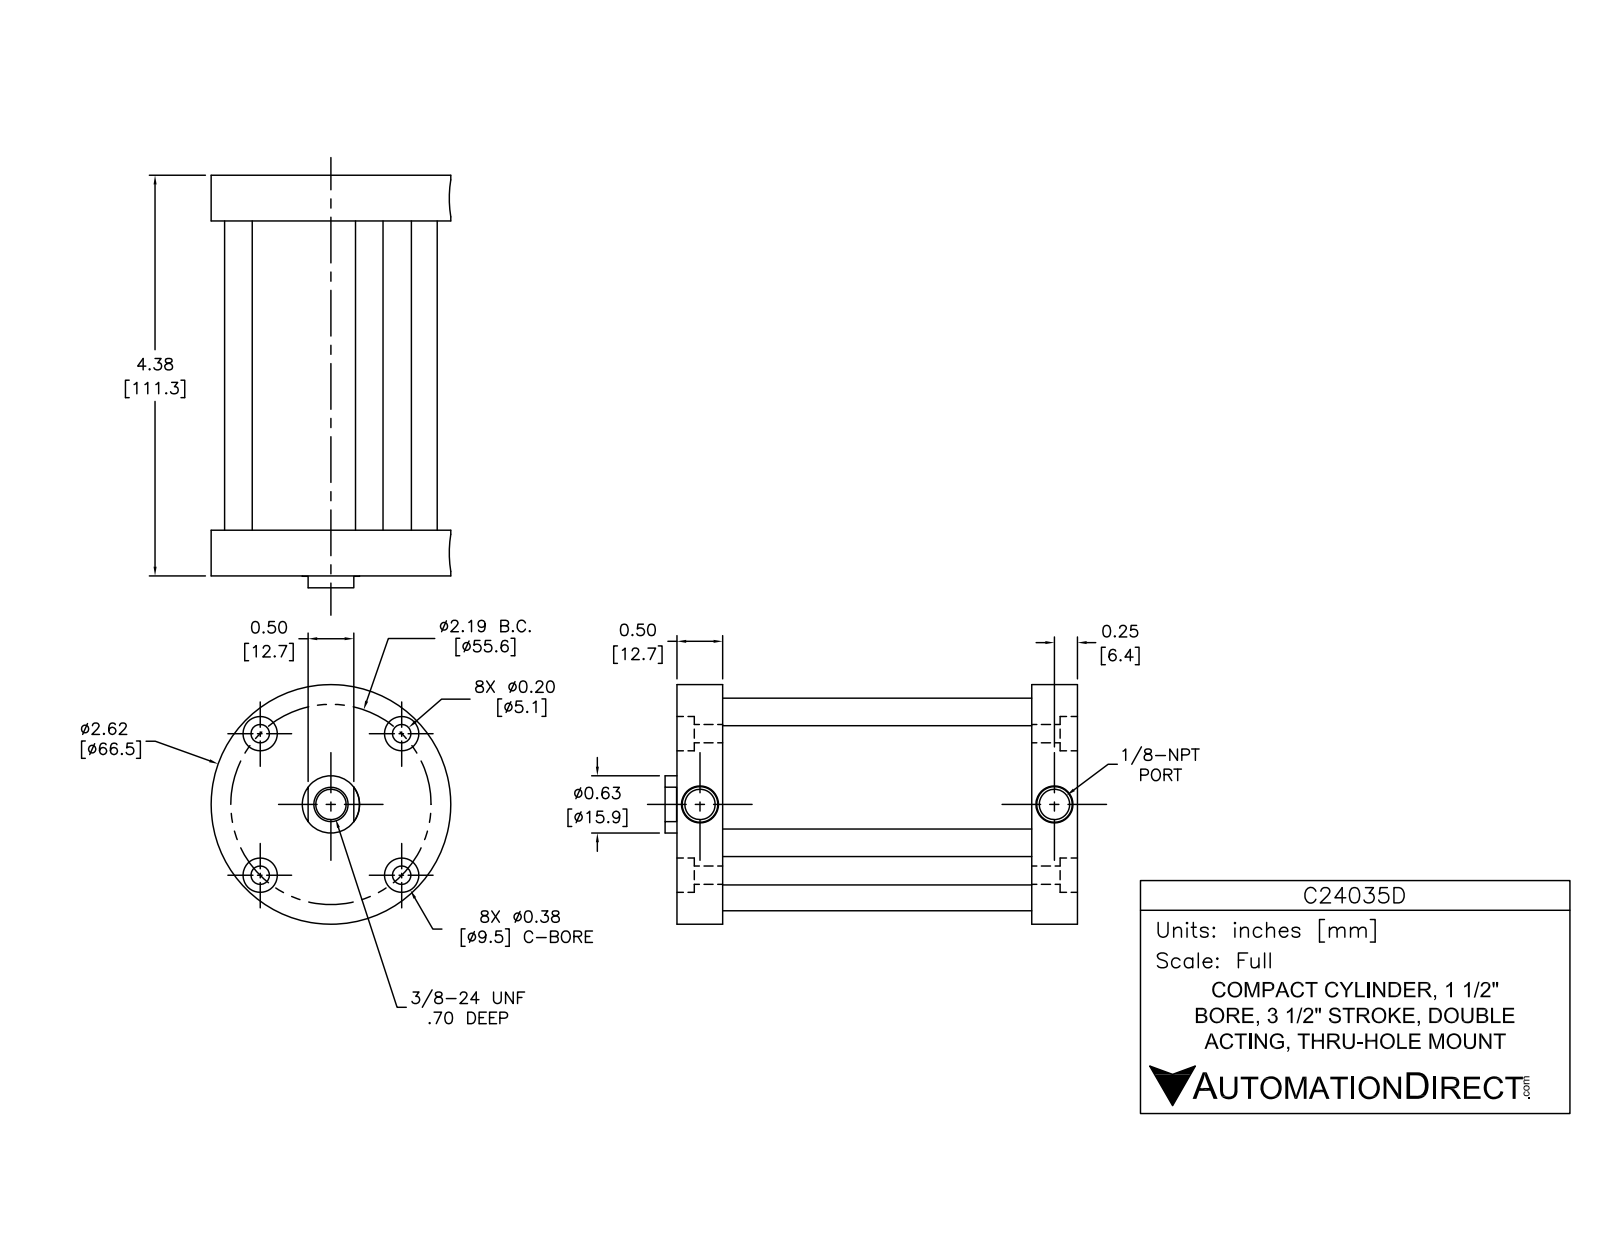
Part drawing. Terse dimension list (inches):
name: C24035D-FO1_BM_tube; C24035D-FO1_BM_heads (2); C24035D; C24035D-FO1_BM_heads (+3 more)
written by: SolidWorks 2014 (AUTOMOTIVE_DESIGN)
unit: in
bodies: 9 solids, 165 faces (49 planar, 98 cylindrical, 18 other)
size: 4.51 × 2.62 × 2.62
volume: 8.111 in³; area: 107.5 in²
holes: 4× ⌀0.2, 4× ⌀0.218, 4× ⌀0.343, 2× ⌀0.125, 1× ⌀0.33, 1× ⌀0.63, 1× ⌀0.632, 1× ⌀1.503, 1× ⌀1.563
bosses: 4× ⌀0.4, 1× ⌀2.62
face distances: 0.5, 3.88, 0.282, 4.098, 3.598, 0.218, 4.38, 3.38, 3.816, 0.598
hole spacings: 1.095, 1.549, 0.428, 1.217, 1.821, 2.148, 2.19, 2.191
